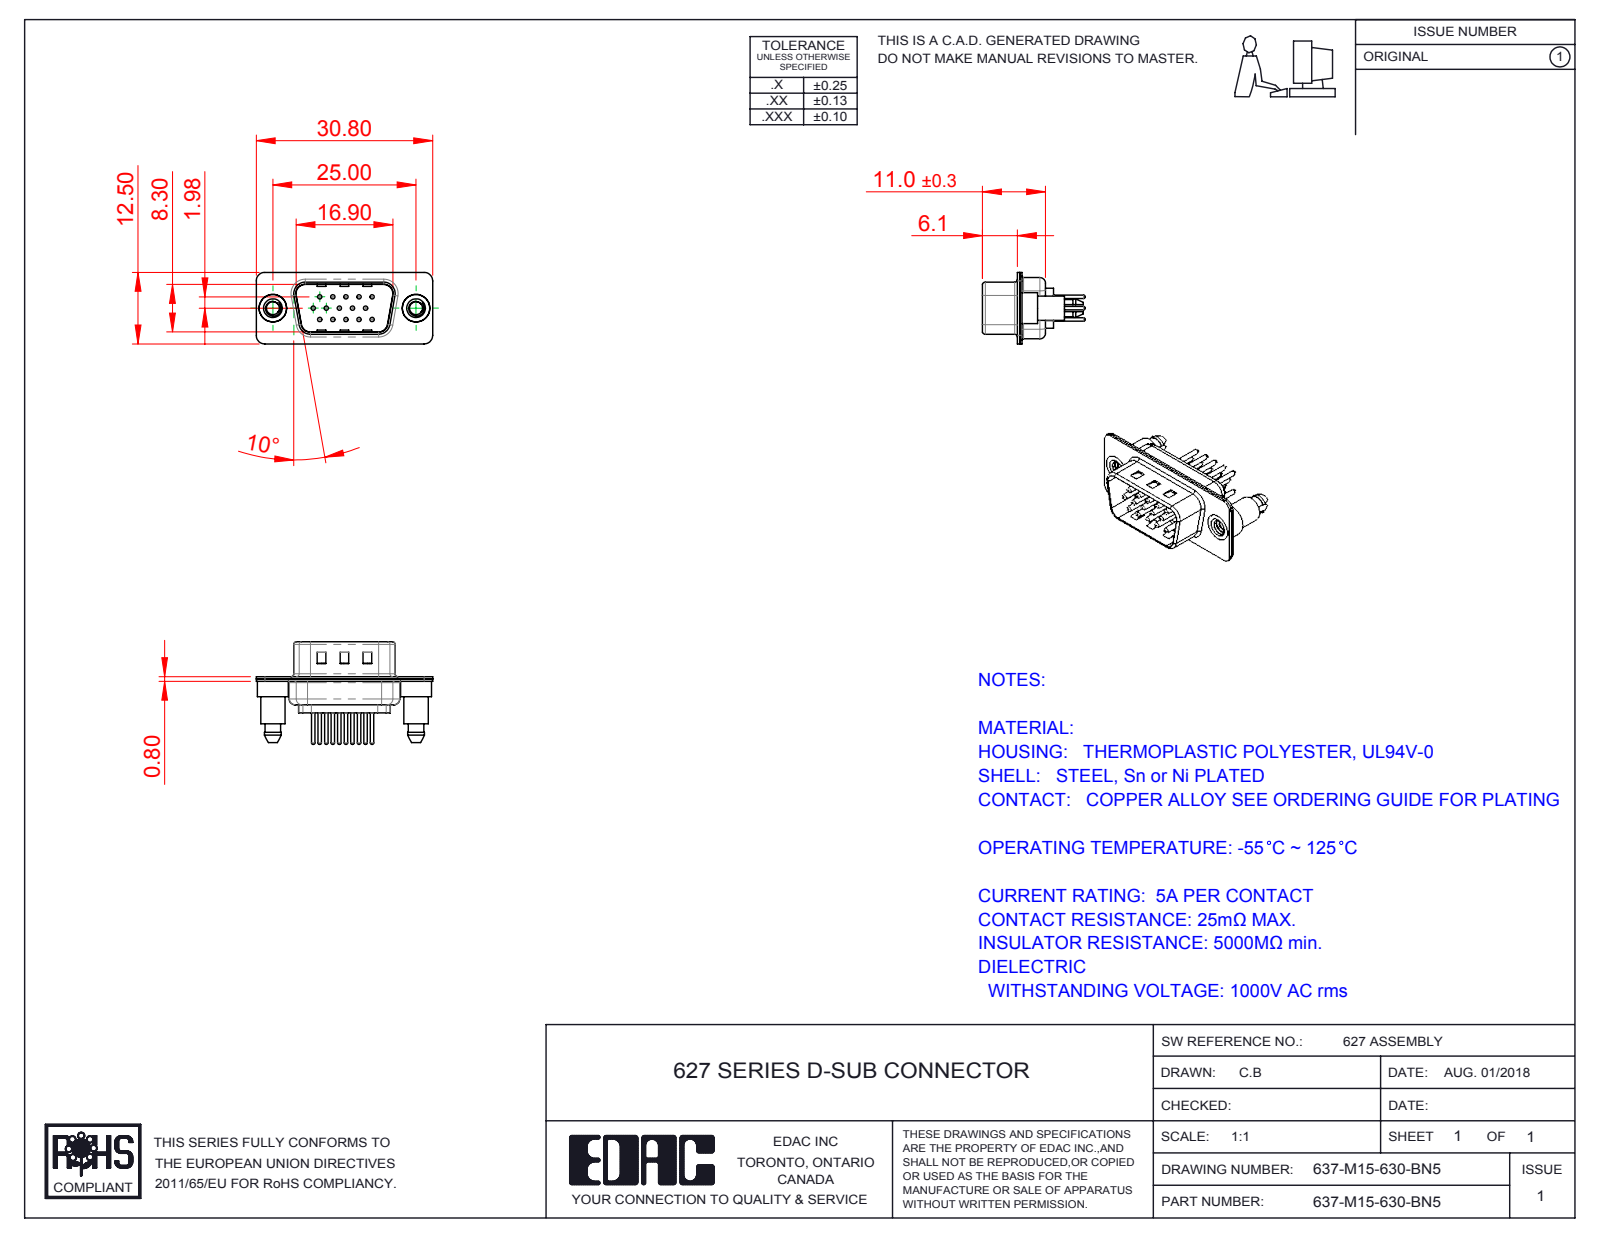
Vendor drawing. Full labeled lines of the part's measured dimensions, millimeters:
Part name (STEP PRODUCT): 637M Shell Front_15 Contacts; 637M Contact Row 1_30; 637M Shell Rear_15 Contacts; 637M Housing_15 Contacts (+4 more)
STEP written by: SolidWorks 2016 (CONFIG_CONTROL_DESIGN)
Units: millimetres
Bodies: 20 solids, 909 faces (228 planar, 371 cylindrical, 310 other)
Overall size (bounding box): 30.8 × 17.9 × 12.5
Volume: 1 483 mm³ · Surface area: 4 425 mm²
Round holes (diameter × count): ⌀0.75 ×15, ⌀1.6 ×15, ⌀2 ×15, ⌀2.26 ×2, ⌀4 ×2, ⌀4.8 ×2
Round bosses / shafts (diameter × count): ⌀1.5 ×15, ⌀0.6 ×15, ⌀5.4 ×2, ⌀4.9 ×2, ⌀4.25 ×2
Partial cylindrical surfaces — rounded edges, fillets, slot ends (radius × count): R1.5 ×18, R2 ×12, R1.6 ×10, R0.5 ×8, R0.25 ×4, R0.6 ×4, R0.65 ×4, R0.9 ×4
Main face-to-face distances: 0.4, 0.8, 9.5, 9.1, 0.65, 8.7, 9.9, 6.3, 1.4, 0.75
Hole centre spacings: 3.96, 2.28, 2.29, 4.57, 6.05, 6.86, 7.92, 6.04
